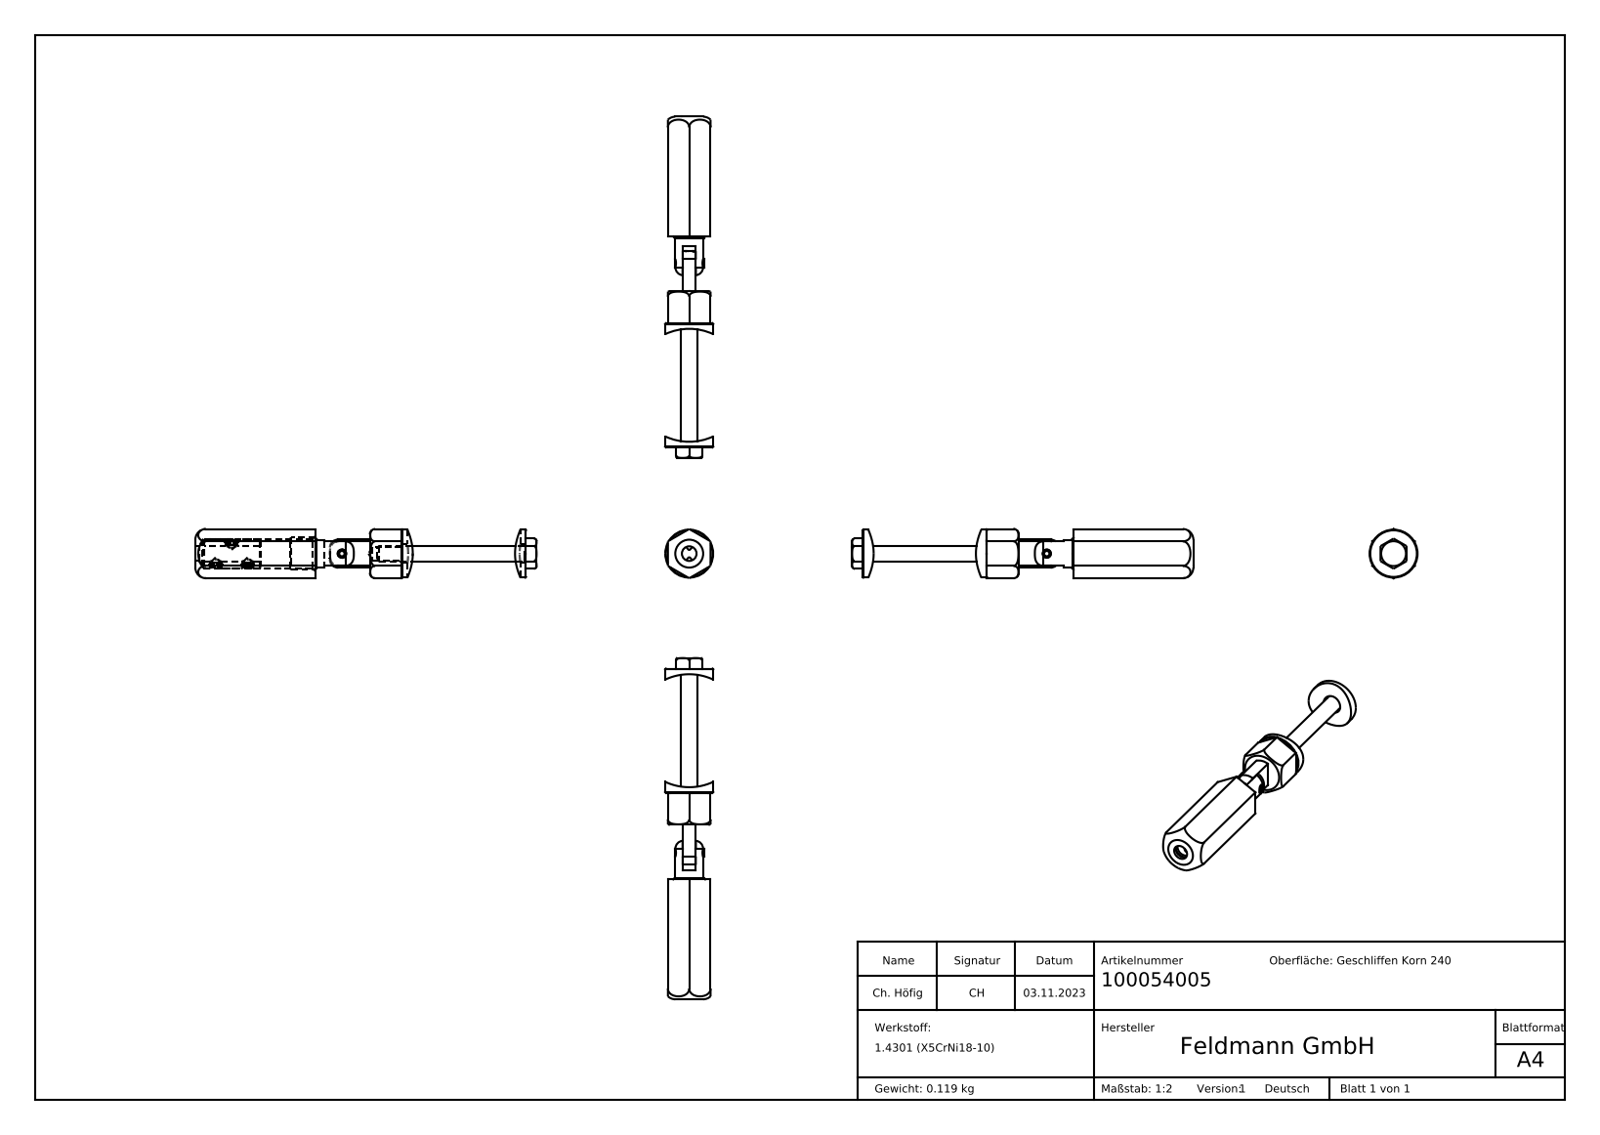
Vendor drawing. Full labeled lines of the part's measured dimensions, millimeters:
Part name (STEP PRODUCT): 10005400X Teil6_100054005 Teil6; 10005400X Teil1_100054x05 Teil1; 10005400X Teil5_100054x05 Teil5; 10005400X Teil8_100054x05 Teil8 (+5 more)
STEP written by: SolidWorks 2018 (CONFIG_CONTROL_DESIGN)
Units: millimetres
Bodies: 11 solids, 339 faces (177 planar, 28 cylindrical, 134 other)
Overall size (bounding box): 128.12 × 18.48 × 18
Volume: 15 060 mm³ · Surface area: 11 415 mm²
Round holes (diameter × count): ⌀4.2 ×3, ⌀2 ×1, ⌀3.1 ×1, ⌀3.2 ×1, ⌀5 ×1, ⌀5.5 ×1, ⌀6 ×1, ⌀7 ×1, ⌀11 ×1
Round bosses / shafts (diameter × count): ⌀5 ×3, ⌀18 ×1, ⌀12 ×1, ⌀10.8 ×1, ⌀10.4 ×1, ⌀3 ×1
Partial cylindrical surfaces — rounded edges, fillets, slot ends (radius × count): R5.25 ×1, R21.2 ×1
Main face-to-face distances: 16, 5.55, 10.45, 46.6, 5.5, 10.5, 4.95, 12.9, 3.1, 4.9
Hole centre spacings: 6, 12
